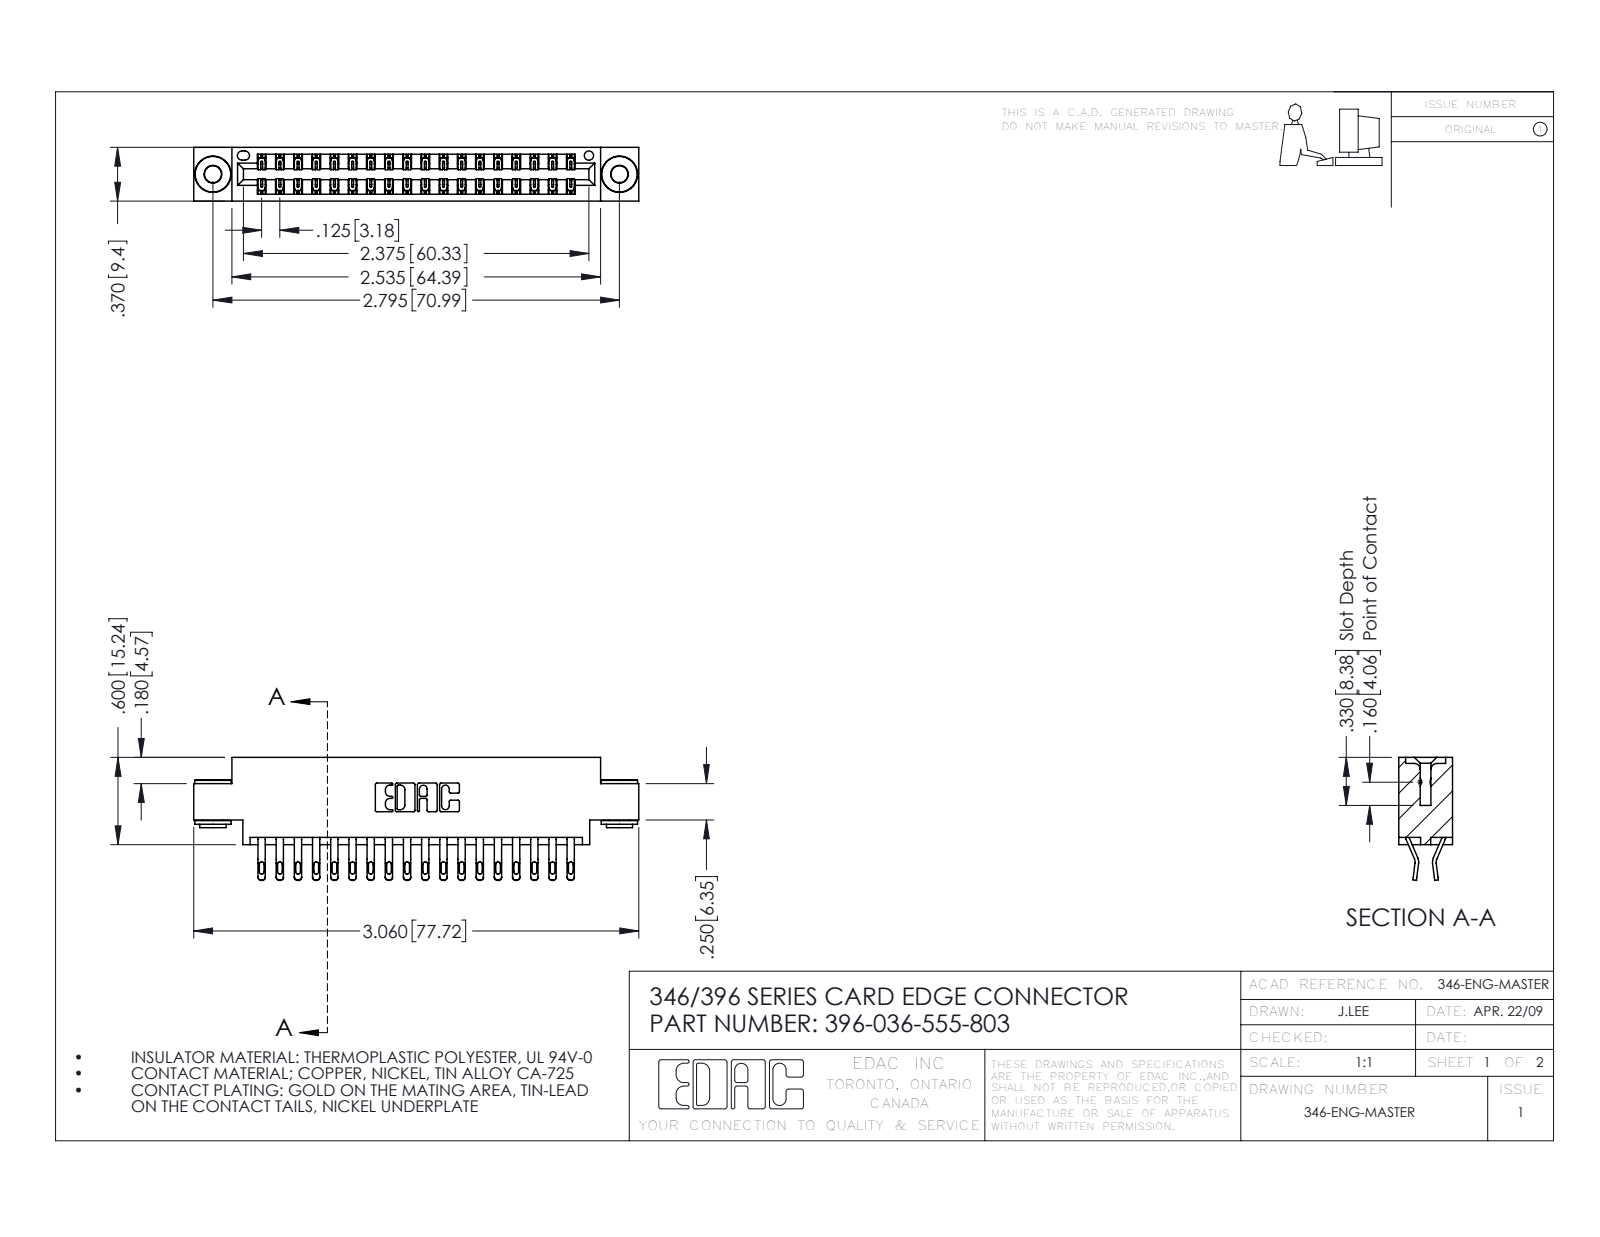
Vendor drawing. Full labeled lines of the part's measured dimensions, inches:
Part name (STEP PRODUCT): 345-250-002_345-250-002-102; 345-292-001_555 Tail; 346 Part_0.170 Offset - 0.156 Dia-TH; 396-036-555-803
STEP written by: SolidWorks 2016 (CONFIG_CONTROL_DESIGN)
Units: inches
Bodies: 39 solids, 2252 faces (1278 planar, 966 cylindrical, 8 other)
Overall size (bounding box): 3.06 × 0.845 × 0.37
Volume: 0.449 in³ · Surface area: 16.29 in²
Round holes (diameter × count): ⌀0.116 ×2, ⌀0.156 ×2, ⌀0.064 ×1
Round bosses / shafts (diameter × count): ⌀0.25 ×2, ⌀0.18 ×2, ⌀0.136 ×2
Partial cylindrical surfaces — rounded edges, fillets, slot ends (radius × count): R0.016 ×72, R0.02 ×72, R0.006 ×54, R0.01 ×22, R0.007 ×6, R0.031 ×6, R0.026 ×3, R0.01 ×2
Main face-to-face distances: 0.048, 0.322, 0.37, 0.25, 0.025, 0.275, 0.072, 0.298, 0.148, 0.222
Hole centre spacings: 0.246, 2.588, 2.795
